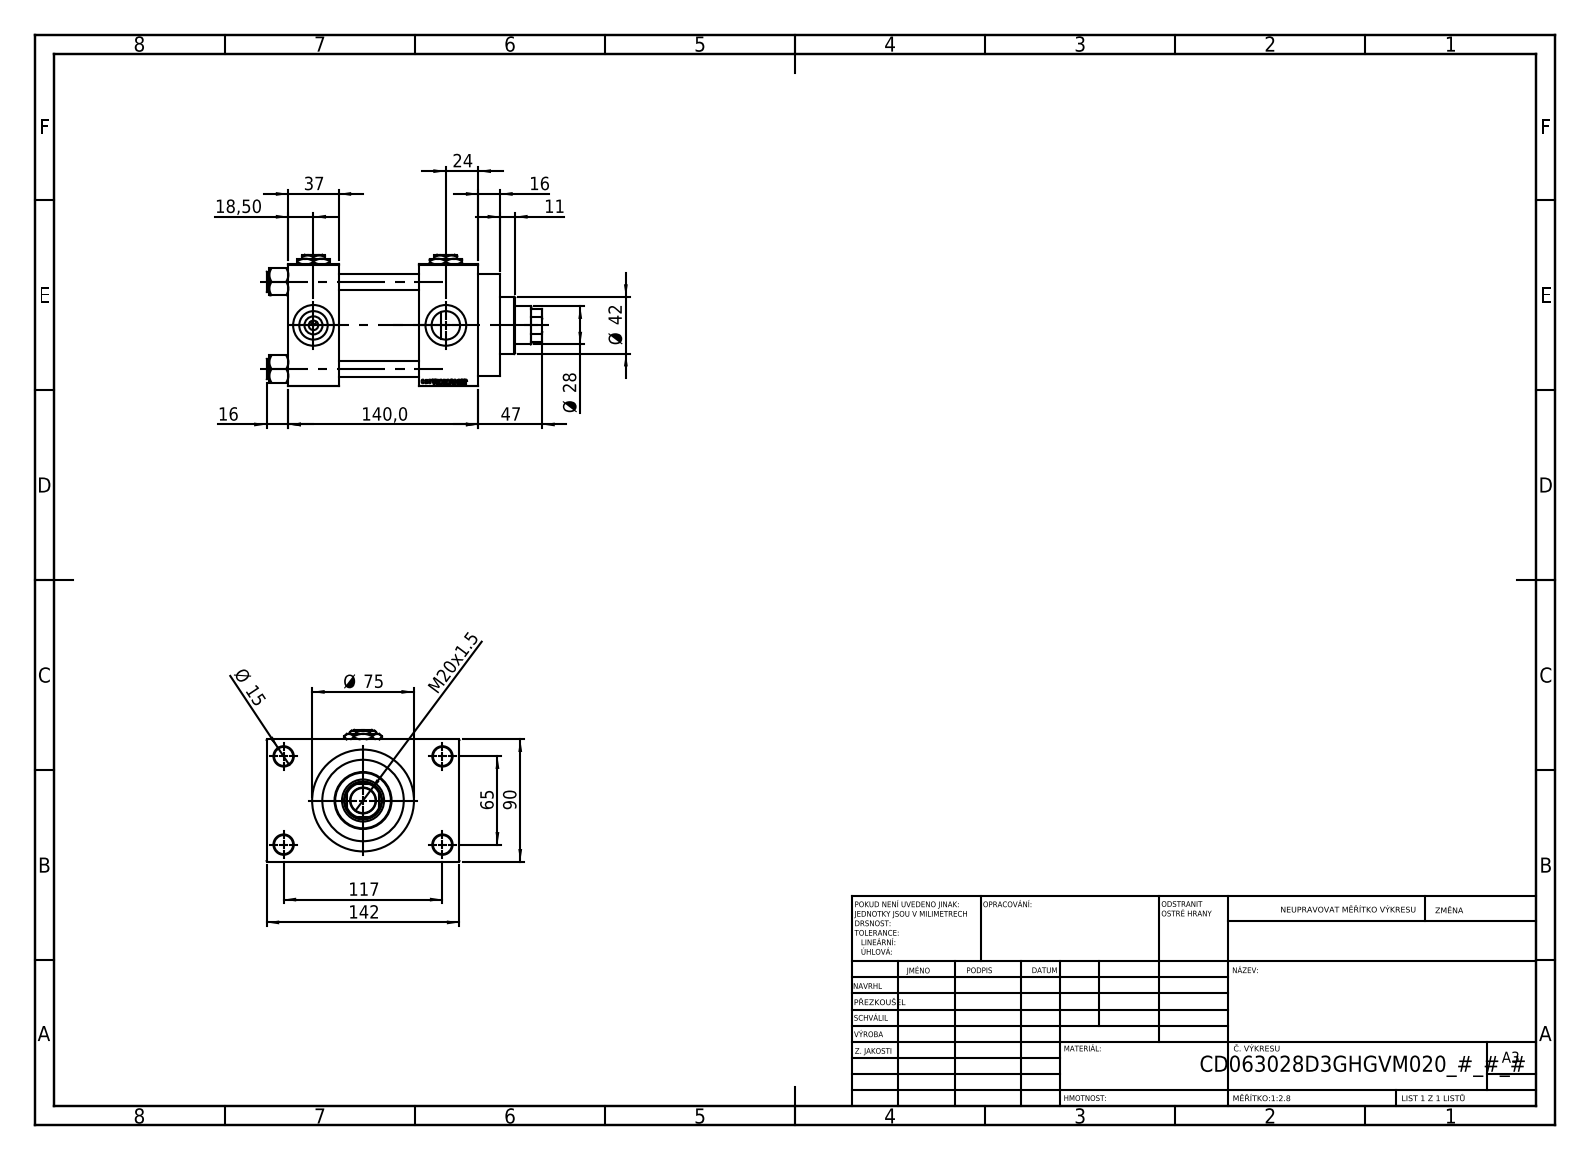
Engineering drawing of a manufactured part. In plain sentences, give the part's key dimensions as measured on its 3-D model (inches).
The part is named "Zatka_pro_OIL_PORT; V215CD_VCP_D; V215CD_D_Body; V215CD_NUT_M5_D (+2 more)". Its 3-D file was written by "SolidWorks 2019 (CONFIG_CONTROL_DESIGN)". It is 13 solids with 1204 faces: 545 planar, 99 cylindrical and 560 other. Overall it measures 7.992 by 5.591 by 3.819 inches. Its volume is 66.58 cubic inches and its surface area 317.7 square inches. Round holes: 4 of diameter 0.472, 4 of diameter 0.551, 4 of diameter 0.825, 4 of diameter 1.181, 3 of diameter 0.276, 1 of diameter 0.728, 1 of diameter 1.102, 1 of diameter 1.22, 1 of diameter 1.969, 1 of diameter 2.362, 1 of diameter 2.48. Round bosses or shafts: 4 of diameter 0.591, 1 of diameter 2.953, 1 of diameter 2.717, 1 of diameter 1.654. Partial cylindrical surfaces (rounded edges, fillets, slot ends): 1 of radius 0.531. The main face-to-face distances are 3.543, 2.323, 1.457, 3.78, 5.512, 4.055, 1.732, 1.024, 4.567, 0.63. The hole center spacings are 1.037, 1.79, 2.531, 2.635, 2.748, 3.569, 4.383, 2.559.
